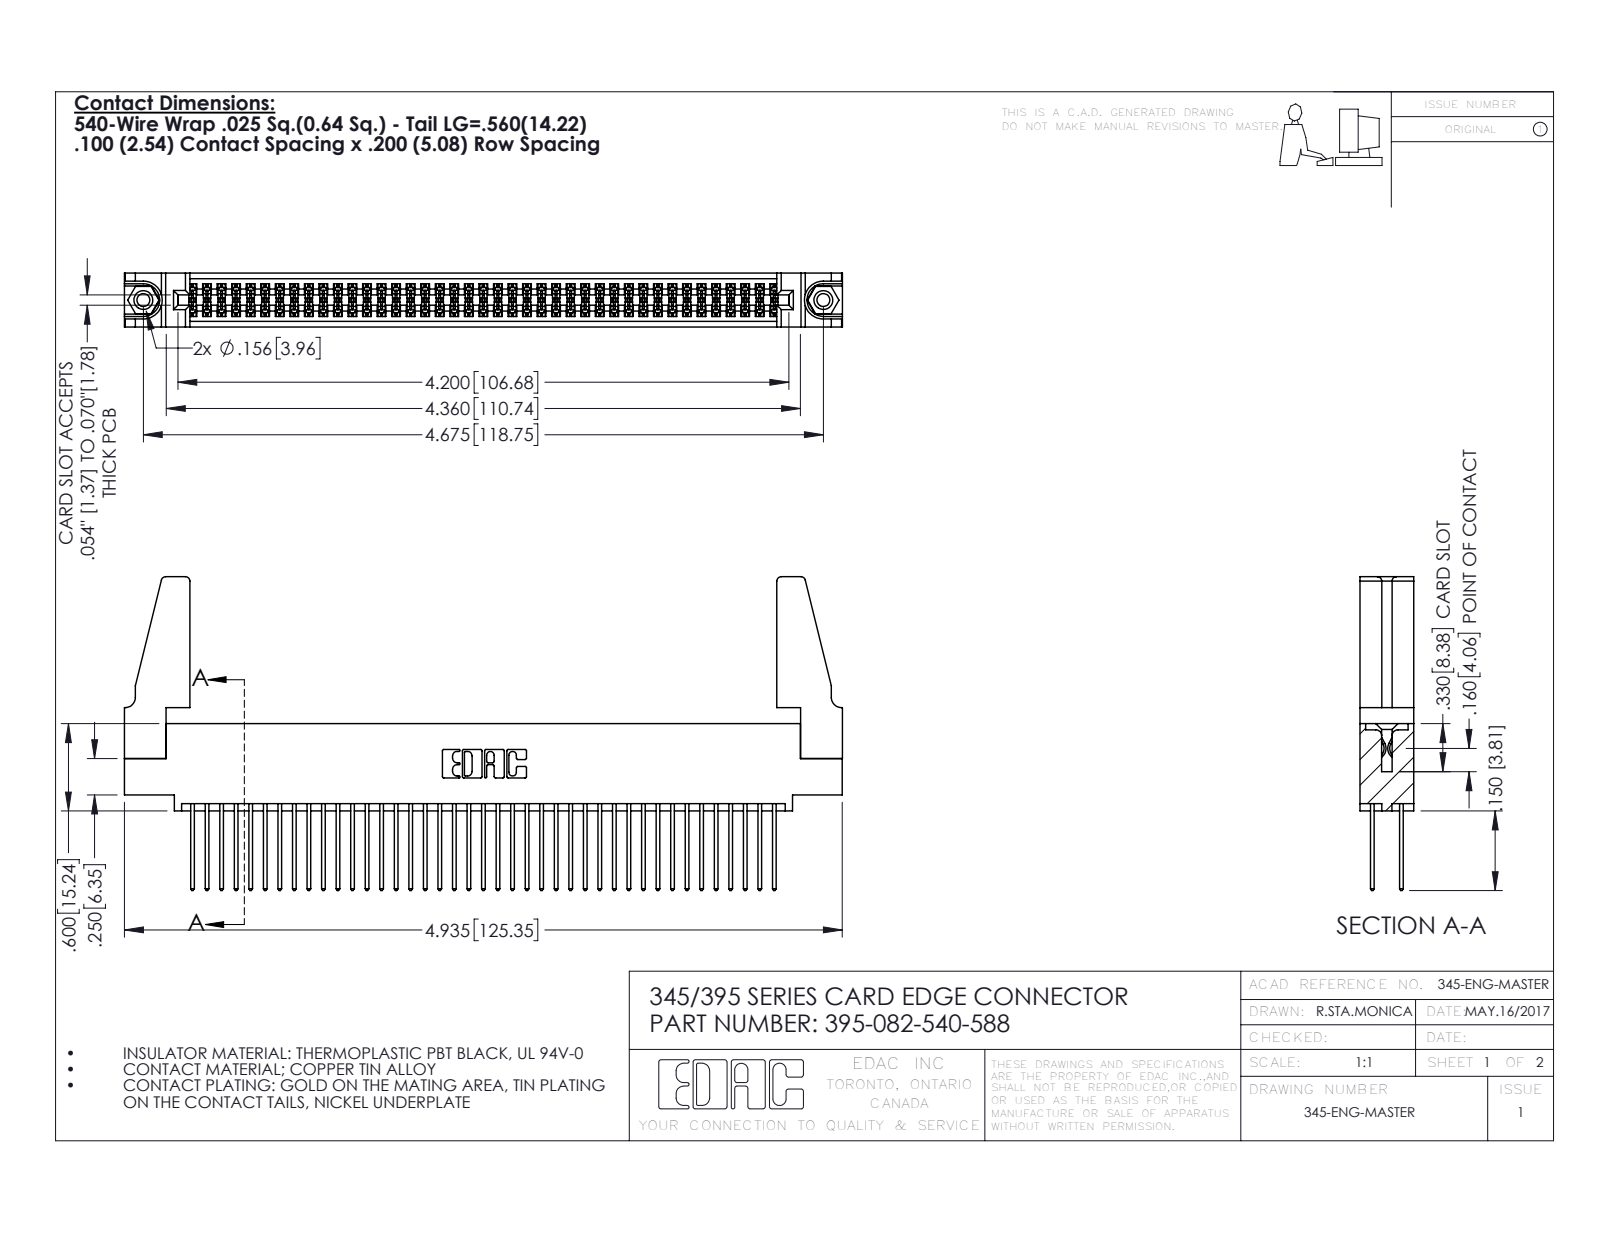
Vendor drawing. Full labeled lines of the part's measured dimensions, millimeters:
Part name (STEP PRODUCT): 345-250-001_345-250-001-102; 345 Part_0.110 Offset - 0.156 Dia-TH; 345-292-001_345-293-140; 345-220-078_345-220-088 (+1 more)
STEP written by: SolidWorks 2016 (CONFIG_CONTROL_DESIGN)
Units: millimetres
Bodies: 87 solids, 4354 faces (2862 planar, 1476 cylindrical, 16 other)
Overall size (bounding box): 125.4 × 54.8 × 9.4
Volume: 15 700 mm³ · Surface area: 22 980 mm²
Round holes (diameter × count): ⌀2.3 ×2, ⌀3.2 ×2, ⌀4 ×2, ⌀1.6 ×1
Round bosses / shafts (diameter × count): ⌀3.9 ×2
Partial cylindrical surfaces — rounded edges, fillets, slot ends (radius × count): R0.2 ×123, R0.3 ×82, R0.3 ×22, R0.8 ×8, R0.2 ×6, R0.8 ×6, R0.7 ×3, R0.4 ×2
Main face-to-face distances: 1.8, 7.6, 5.1, 2.5, 6.9, 0.6, 9.4, 5.7, 4.4, 3.8
Hole centre spacings: 6.9, 112.8, 118.7
